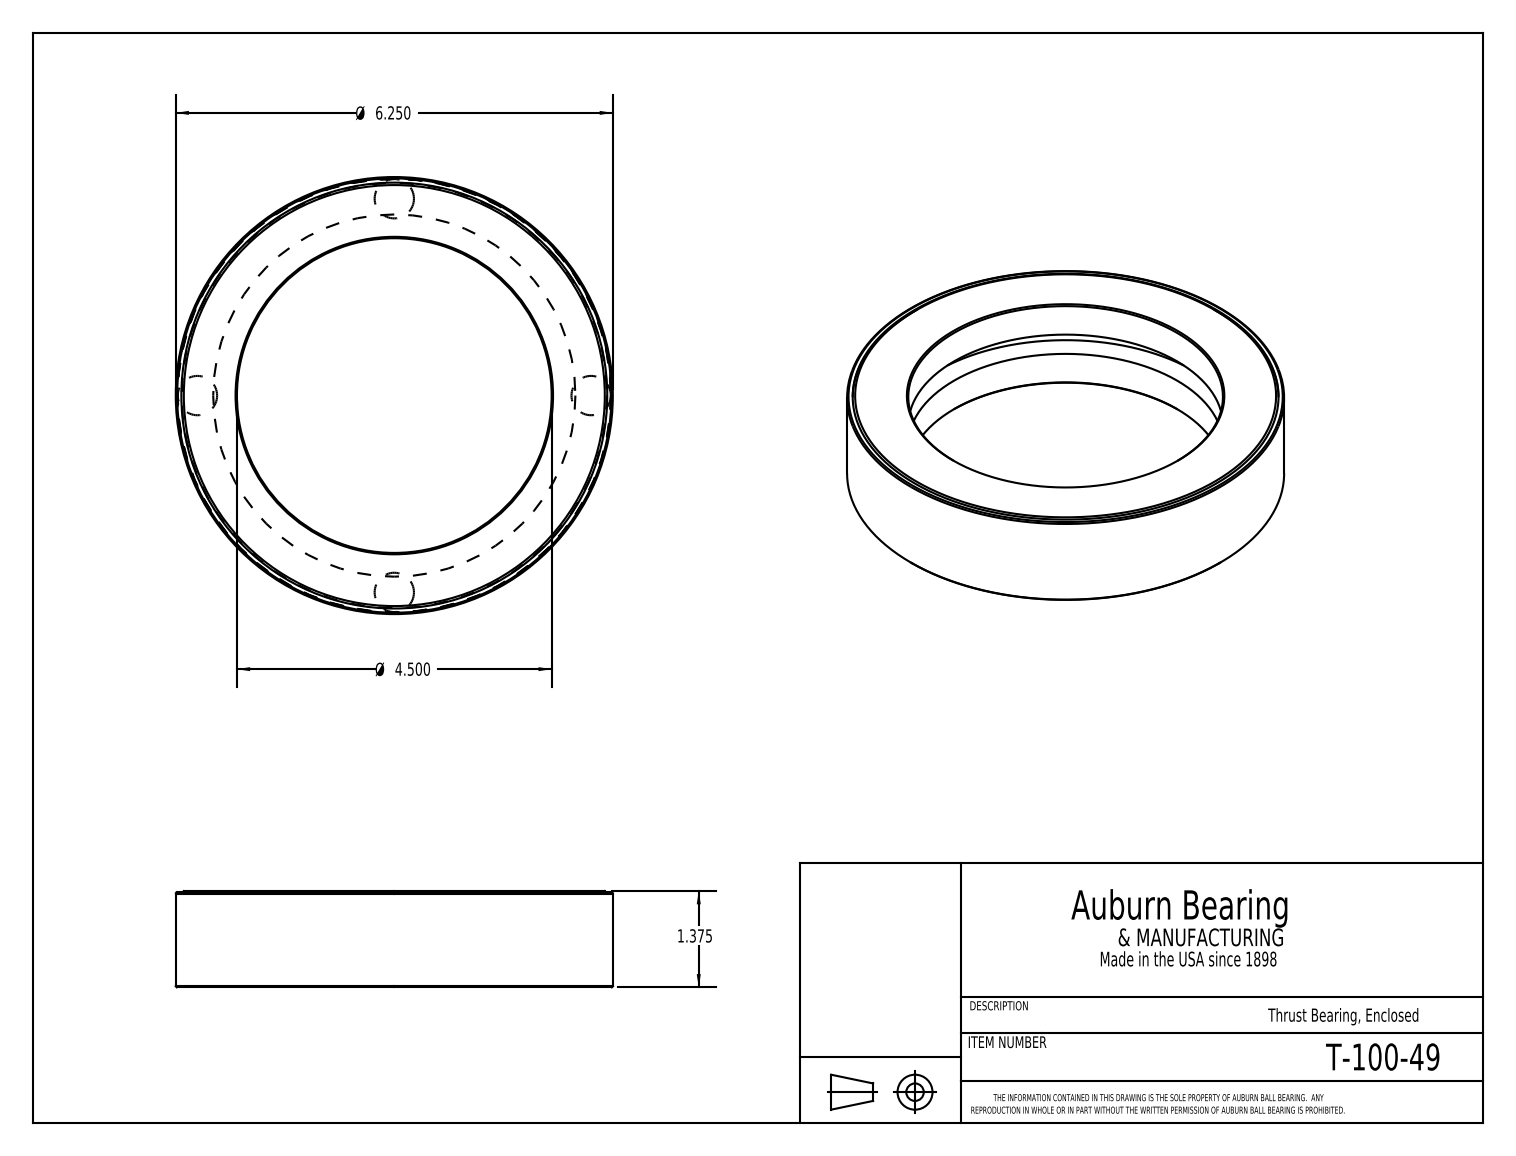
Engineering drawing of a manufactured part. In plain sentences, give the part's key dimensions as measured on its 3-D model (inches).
The part is named "T-100-49". Its 3-D file was written by "SolidWorks 2016 (CONFIG_CONTROL_DESIGN)". It is 6 solids with 26 faces: 7 planar, 7 cylindrical and 12 other. Overall it measures 6.25 by 6.25 by 1.375 inches. Its volume is 8.913 cubic inches and its surface area 113.5 square inches. Round holes: 1 of diameter 5.2, 1 of diameter 6.09, 1 of diameter 6.21. Round bosses or shafts: 1 of diameter 6.25, 1 of diameter 6.196. The main face-to-face distances are 1.375, 0.519, 0.856, 1.34, 0.821, 0.035, 1.36, 0.841, 0.02, 0.015.
